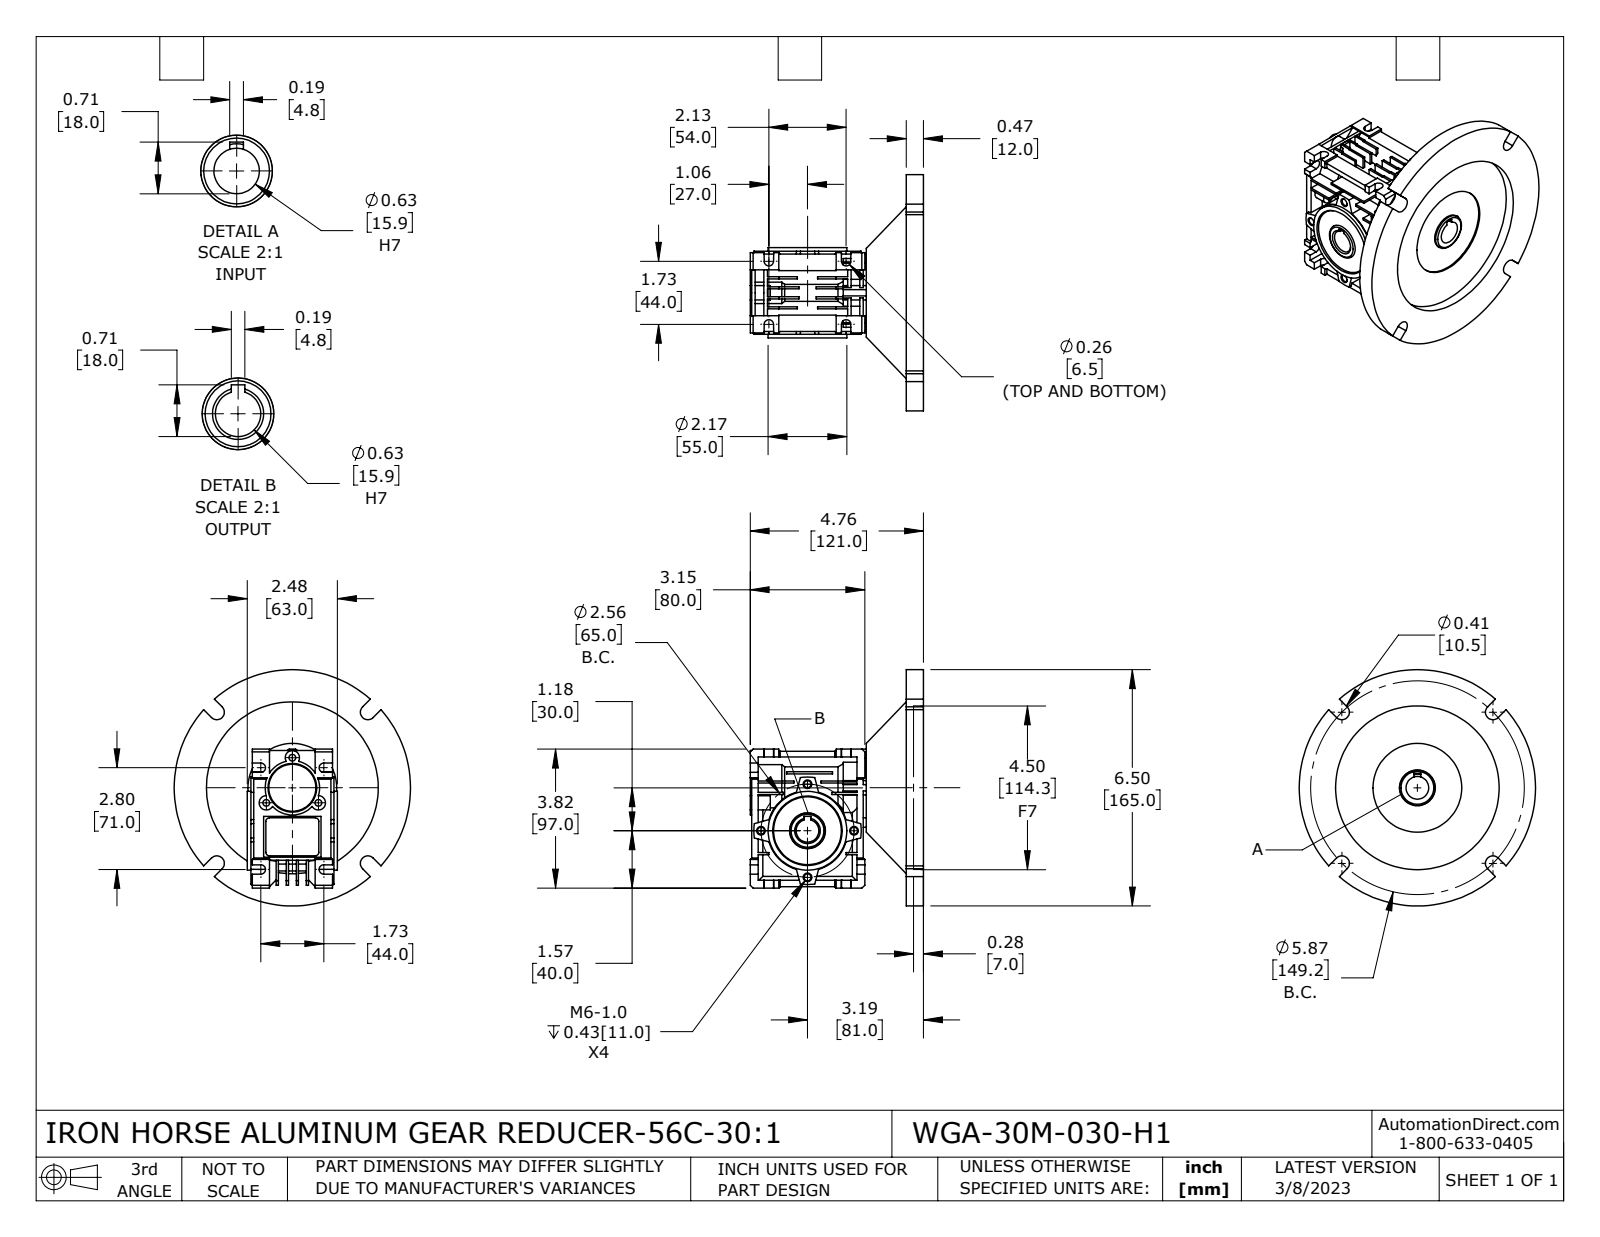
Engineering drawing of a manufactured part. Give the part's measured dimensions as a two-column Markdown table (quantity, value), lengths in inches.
| quantity | value |
| --- | --- |
| part name | WGA-30M-030-H1 |
| STEP written by | SolidWorks 2021 (CONFIG_CONTROL_DESIGN) |
| units | inches |
| bodies | 1 solid, 682 faces (442 planar, 168 cylindrical, 72 other) |
| overall size | 6.496 × 6.496 × 4.764 |
| volume | 39.8 in³ |
| surface area | 198.1 in² |
| round holes (diameter × count) | 0.194 × 4, 0.194 × 4, 0.183 × 3, 0.625 × 2, 2.441 × 1, 4.5 × 1 |
| round bosses / shafts (diameter × count) | 6.496 × 1, 2.205 × 1, 2.165 × 1, 1.496 × 1, 0.984 × 1 |
| partial cylindrical surfaces (radius × count) | 0.128 × 8, 0.197 × 7, 0.098 × 4, 0.207 × 4, 0.374 × 1, 0.669 × 1, 0.846 × 1, 1.476 × 1 |
| main face-to-face distances | 0.276, 0.059, 0.039, 0.472, 0.217, 0.197, 0.177, 0.551, 0.335, 0.157 |
| hole center spacings | 1.28, 1.809, 0.827, 1.432, 2.559, 1.432 |
